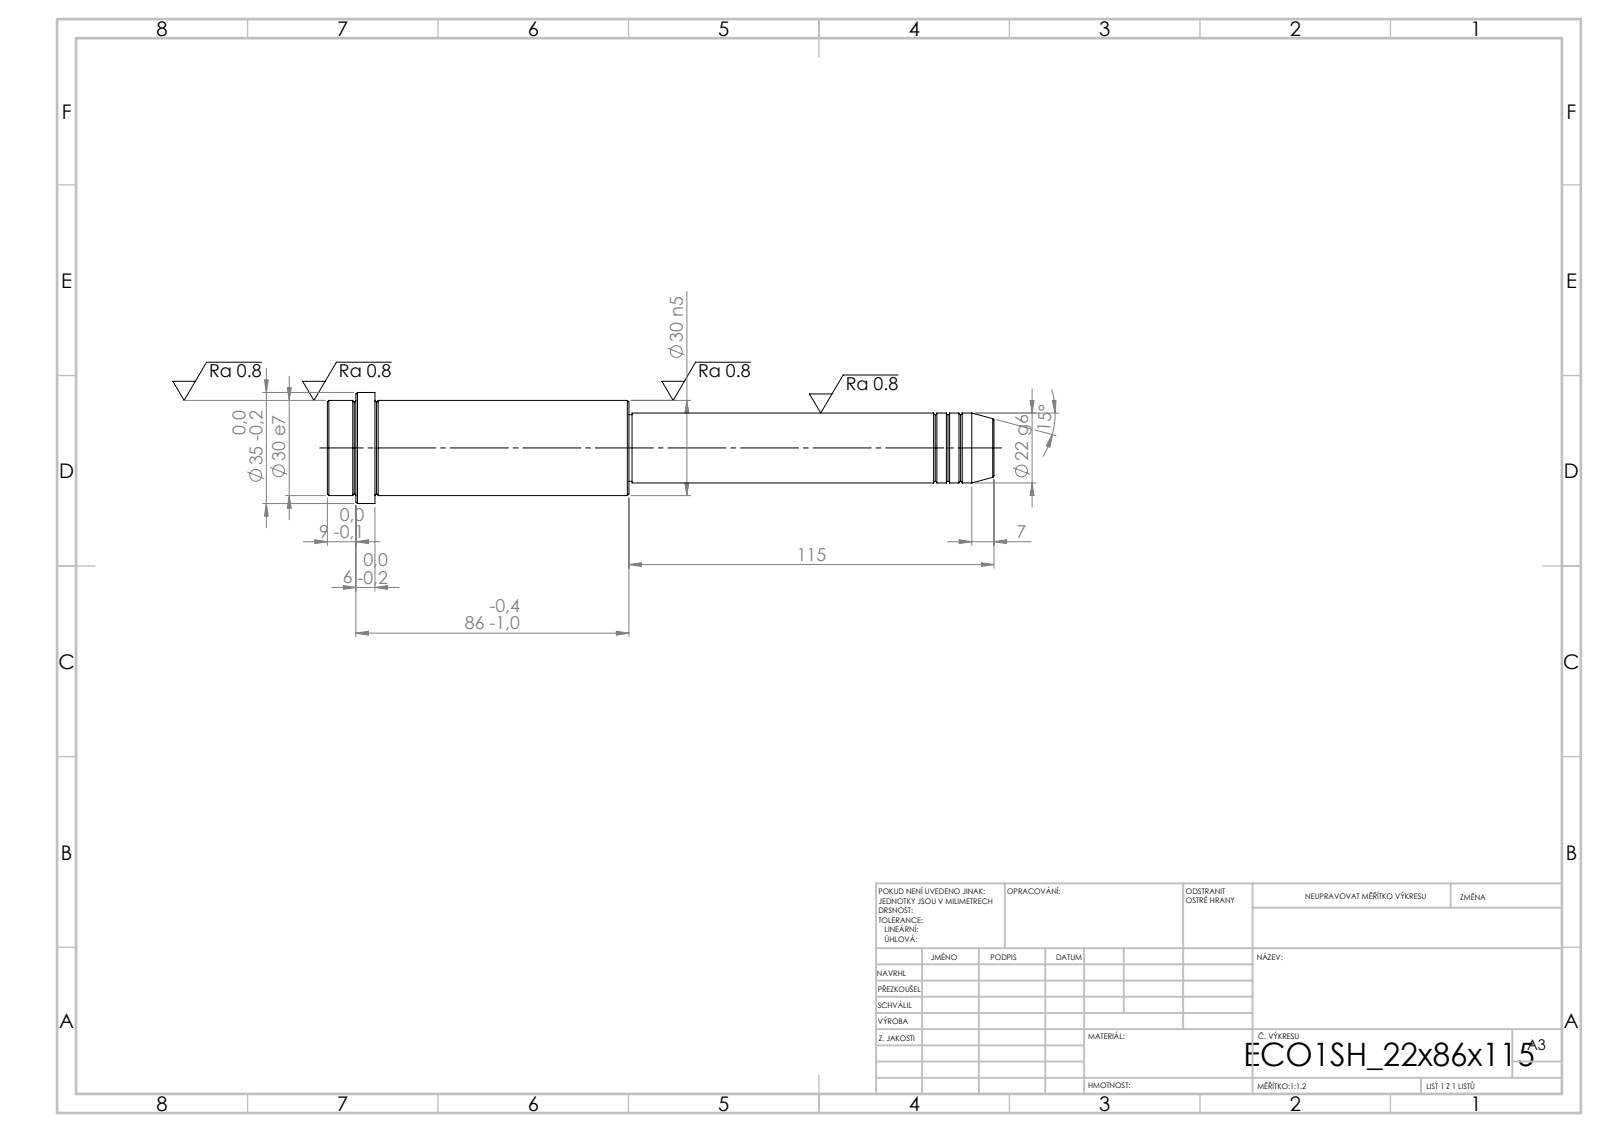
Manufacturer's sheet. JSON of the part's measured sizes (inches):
{"step_written_by": "SolidWorks 2019 (CONFIG_CONTROL_DESIGN)", "units": "inches", "bodies": {"solids": 1, "faces": 52, "planar": 6, "cylindrical": 16, "other": 30}, "overall_size": [8.268, 1.378, 1.378], "volume_in3": 6.819, "surface_area_in2": 29.38, "round_bosses_or_shafts": [[1.378, 1], [1.181, 1], [0.866, 1], [0.827, 1]], "face_to_face_distances": [3.74, 3.15, 0.591, 4.528, 7.677, 8.268, 7.913, 3.386, 0.236, 0.354]}
